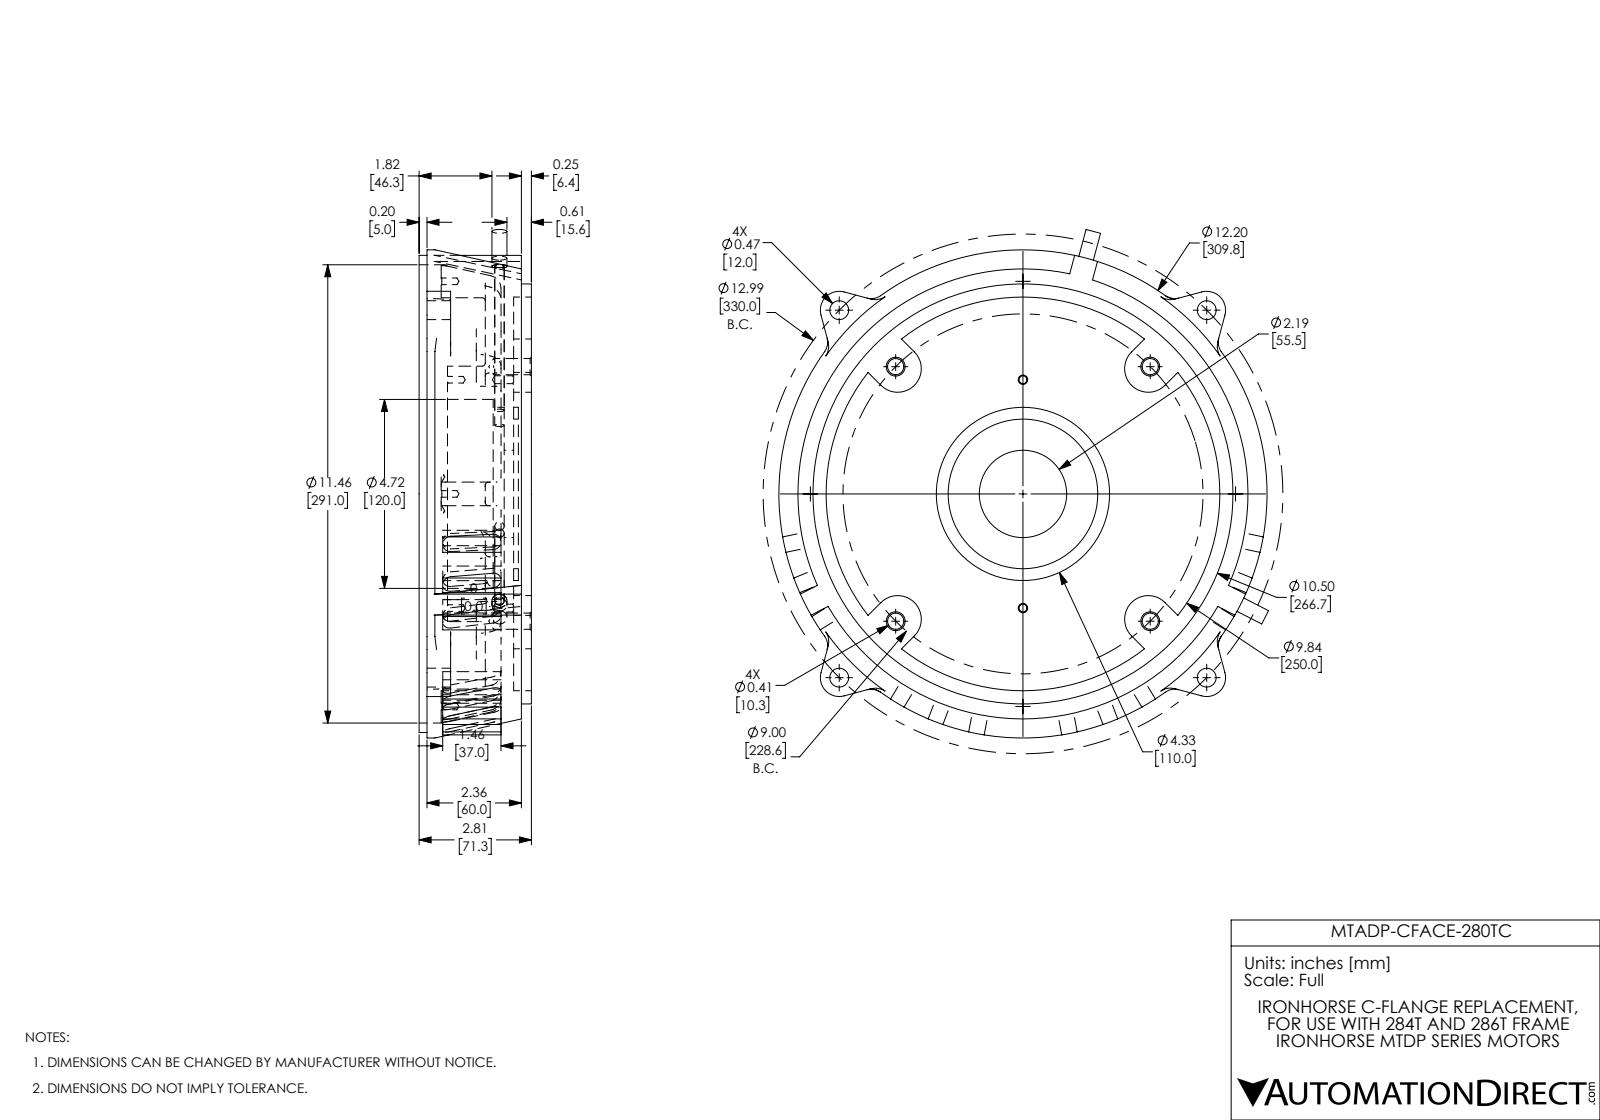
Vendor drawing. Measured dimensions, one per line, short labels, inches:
name: MTADP-CFACE-280
written by: SolidWorks 2017 (AUTOMOTIVE_DESIGN)
unit: in
bodies: 15 solids, 677 faces (166 planar, 243 cylindrical, 268 other)
size: 12.714 × 12.241 × 2.807
volume: 90.35 in³; area: 544.6 in²
holes: 6× ⌀0.165, 4× ⌀0.406, 4× ⌀0.472, 2× ⌀0.197, 2× ⌀0.236, 2× ⌀0.374, 1× ⌀2.185, 1× ⌀3.74, 1× ⌀4.331, 1× ⌀4.724, 1× ⌀9.843, 1× ⌀11.457
bosses: 1× ⌀11.929, 1× ⌀10.5, 1× ⌀5.63
rounds: 56× R0.118, 32× R0.197, 15× R0.079, 8× R0.394, 4× R0.472, 4× R0.492, 4× R0.591, 1× R5.297
face distances: 0.315, 0.394, 0.197, 1.654, 0.079, 0.76, 0.445, 0.51, 0.195, 0.25
hole spacings: 3.831, 4.65, 7.902, 9.073, 10.921, 1.996, 3.199, 4.5
